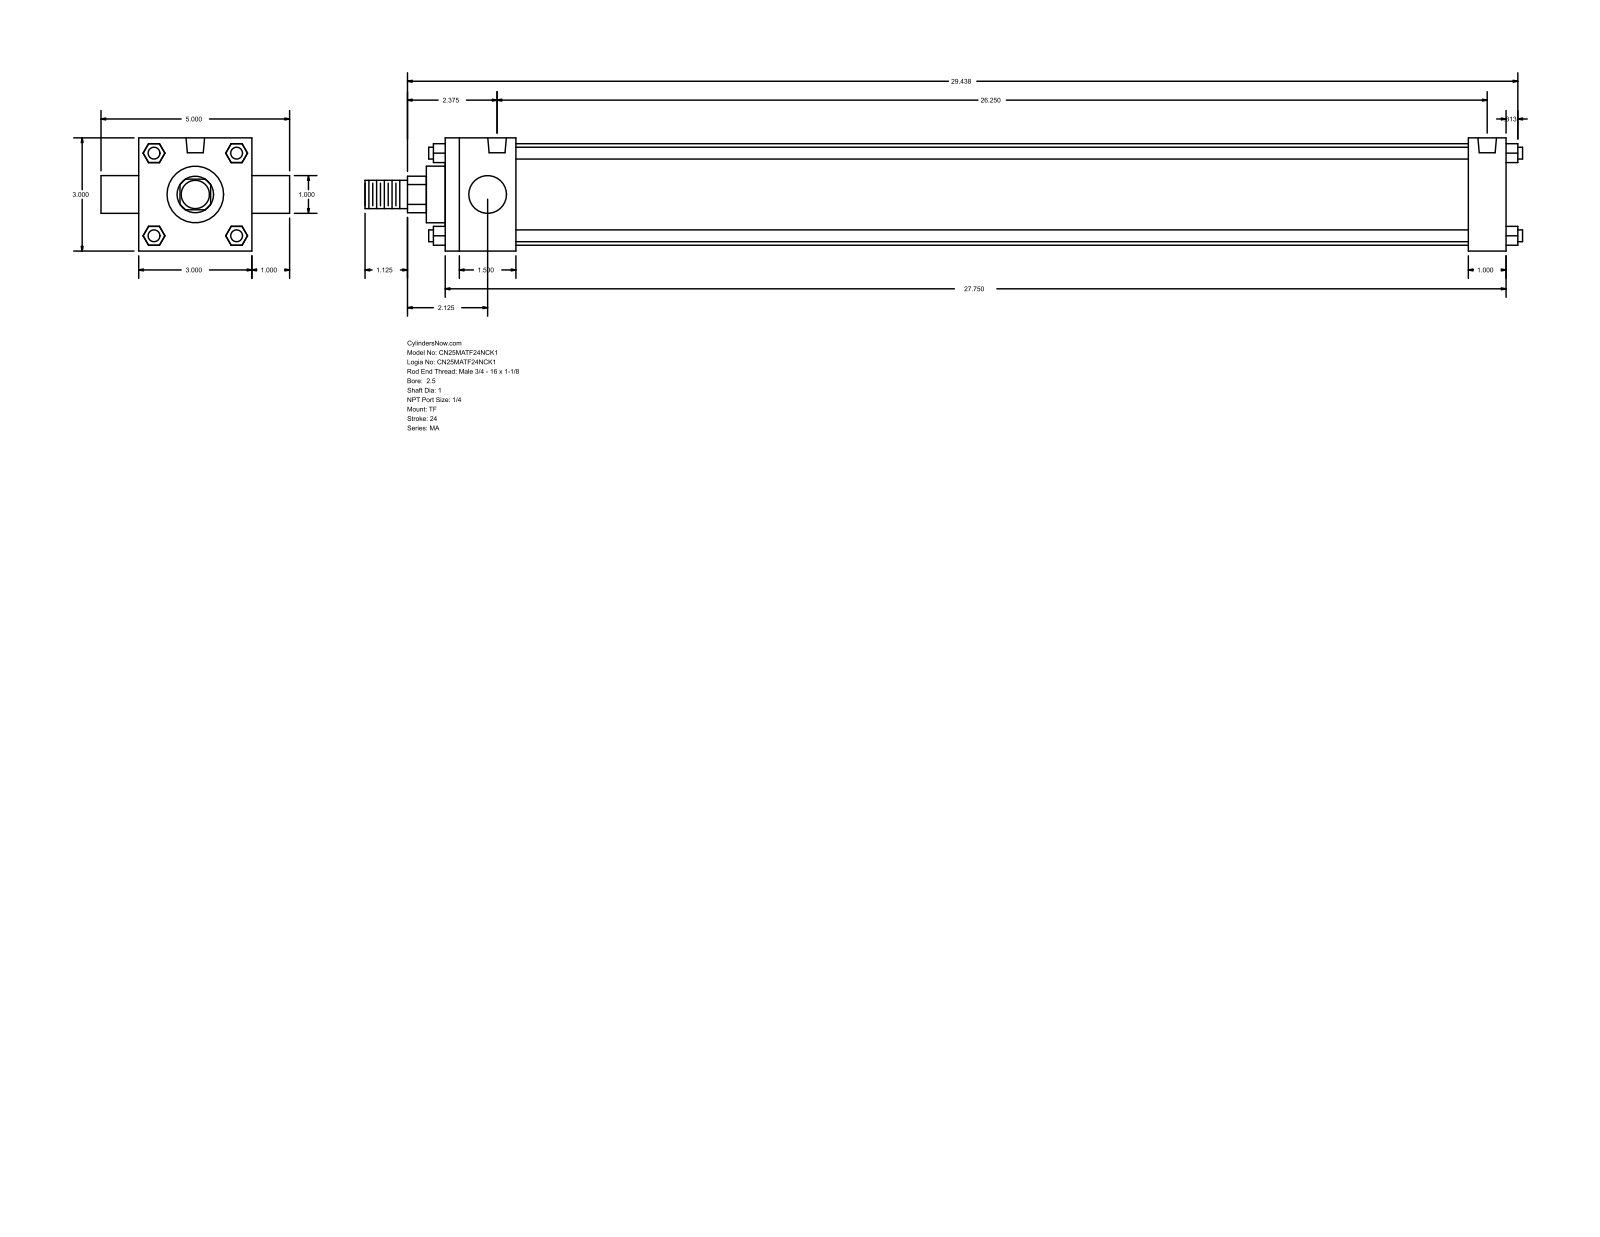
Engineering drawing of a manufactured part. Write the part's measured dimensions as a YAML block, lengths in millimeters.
part_name: "MA_TF__0250_1"
step_written_by: "GSSL Pune (CONFIG_CONTROL_DESIGN)"
units: millimeters
bodies: {solids: 0, faces: 120, planar: 92, cylindrical: 28, other: 0}
overall_size: [779.46, 127, 76.2]
round_holes:
  - {diameter: 7.94, count: 3}
  - {diameter: 12.49, count: 2}
round_bosses_or_shafts:
  - {diameter: 7.94, count: 4}
  - {diameter: 25.4, count: 2}
  - {diameter: 68.33, count: 1}
  - {diameter: 38.1, count: 1}
  - {diameter: 19.05, count: 1}
partial_cylinders:
  - {radius: 12.29, count: 1}
face_to_face_distances: [76.2, 714.37, 12.7, 47.63, 688.98, 641.35, 666.74, 25.39, 101.6, 25.4]
hole_center_spacings: [666.75]
